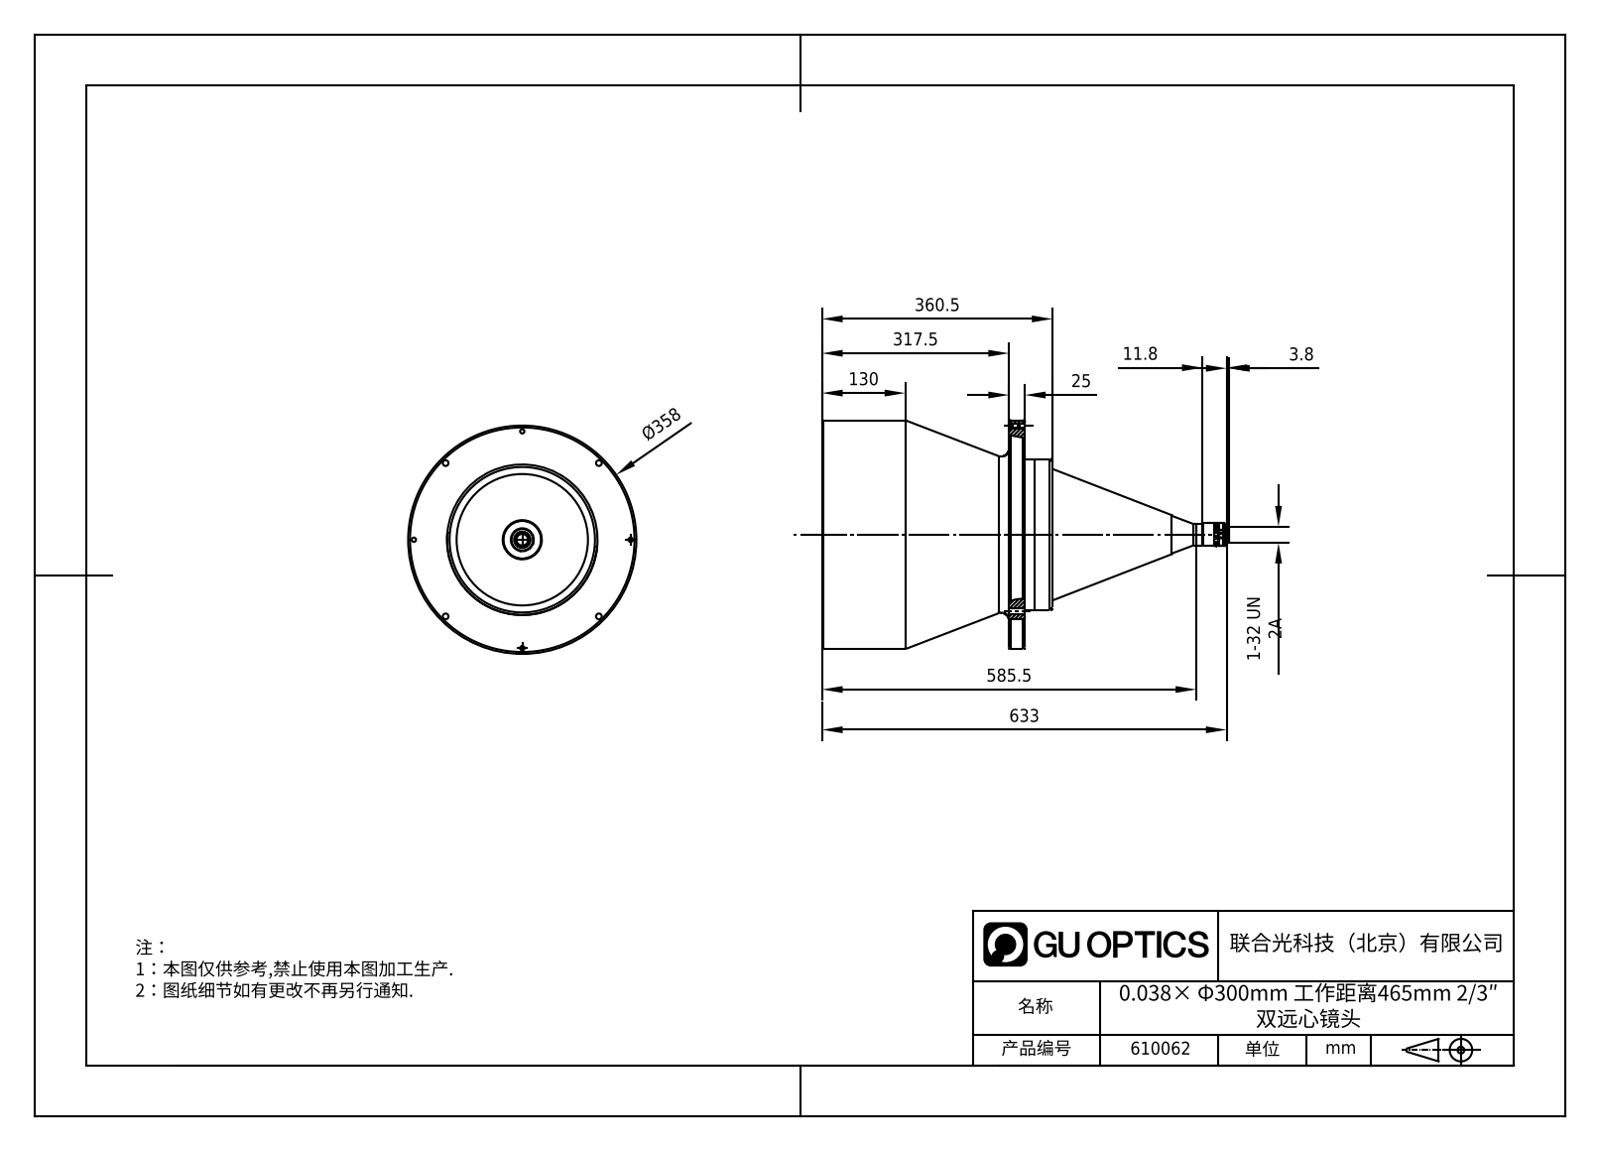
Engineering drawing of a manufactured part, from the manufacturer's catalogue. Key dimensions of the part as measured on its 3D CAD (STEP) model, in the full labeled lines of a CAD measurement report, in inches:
Part name (STEP PRODUCT): DTCM230-300S-AL
STEP written by: SolidWorks 2017 (CONFIG_CONTROL_DESIGN)
Units: inches
Bodies: 1 solid, 280 faces (24 planar, 158 cylindrical, 98 other)
Overall size (bounding box): 25.076 × 14.094 × 14.094
Volume: 1 920 in³ · Surface area: 1 069 in²
Round holes (diameter × count): ⌀0.268 ×4, ⌀0.354 ×4, ⌀0.098 ×3, ⌀0.728 ×1, ⌀0.866 ×1, ⌀8.11 ×1, ⌀13.386 ×1
Round bosses / shafts (diameter × count): ⌀14.094 ×1, ⌀9.291 ×1, ⌀1.417 ×1, ⌀1.378 ×1, ⌀1.339 ×1, ⌀1.335 ×1, ⌀1 ×1
Partial cylindrical surfaces — rounded edges, fillets, slot ends (radius × count): R0.118 ×26, R0.079 ×24, R0.157 ×7, R0.085 ×4, R0.04 ×1, R0.055 ×1, R0.094 ×1
Main face-to-face distances: 0.984, 2.677, 1.693, 11.516, 12.5, 14.193, 24.922, 13.406, 12.422, 10.729
Hole centre spacings: 5.122, 6.693, 9.465, 12.367, 13.386, 13.386
